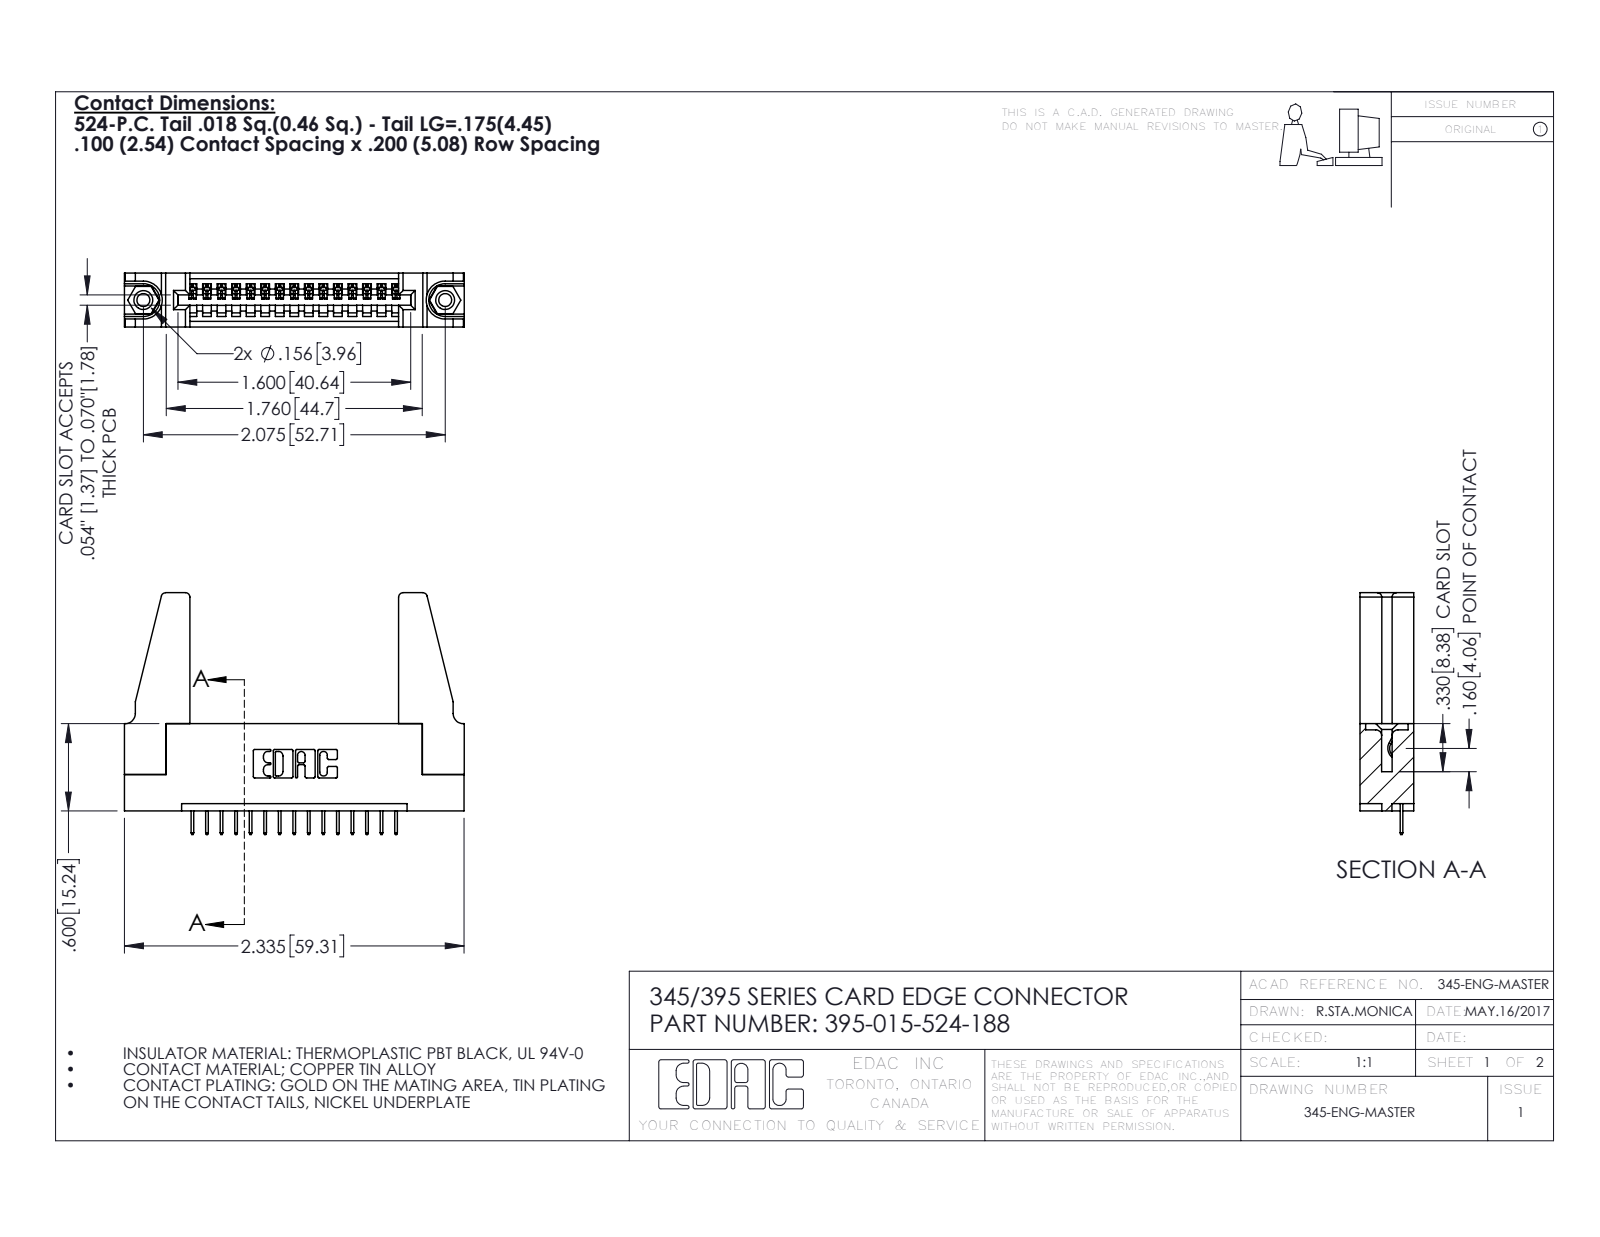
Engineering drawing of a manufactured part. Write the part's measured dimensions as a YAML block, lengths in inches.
part_name: "345 Part_Flush Mounting Lugs - 0.156 Dia-TH; 395-015-524-188; 345-250-001_345-250-001-102; 345-220-078_345-220-088 (+1 more)"
step_written_by: "SolidWorks 2016 (CONFIG_CONTROL_DESIGN)"
units: inches
bodies: {solids: 20, faces: 1180, planar: 842, cylindrical: 322, other: 16}
overall_size: [2.336, 1.662, 0.37]
volume: 0.525
surface_area: 15.02
round_holes:
  - {diameter: 0.089, count: 2}
  - {diameter: 0.125, count: 2}
  - {diameter: 0.156, count: 2}
  - {diameter: 0.064, count: 1}
round_bosses_or_shafts:
  - {diameter: 0.155, count: 2}
partial_cylinders:
  - {radius: 0.006, count: 30}
  - {radius: 0.01, count: 22}
  - {radius: 0.03, count: 8}
  - {radius: 0.007, count: 6}
  - {radius: 0.031, count: 6}
  - {radius: 0.026, count: 3}
  - {radius: 0.031, count: 2}
  - {radius: 0.04, count: 2}
face_to_face_distances: [0.37, 0.072, 0.298, 0.2, 0.098, 0.272, 0.025, 0.225, 0.148, 0.15]
hole_center_spacings: [0.27, 1.842, 2.075]
